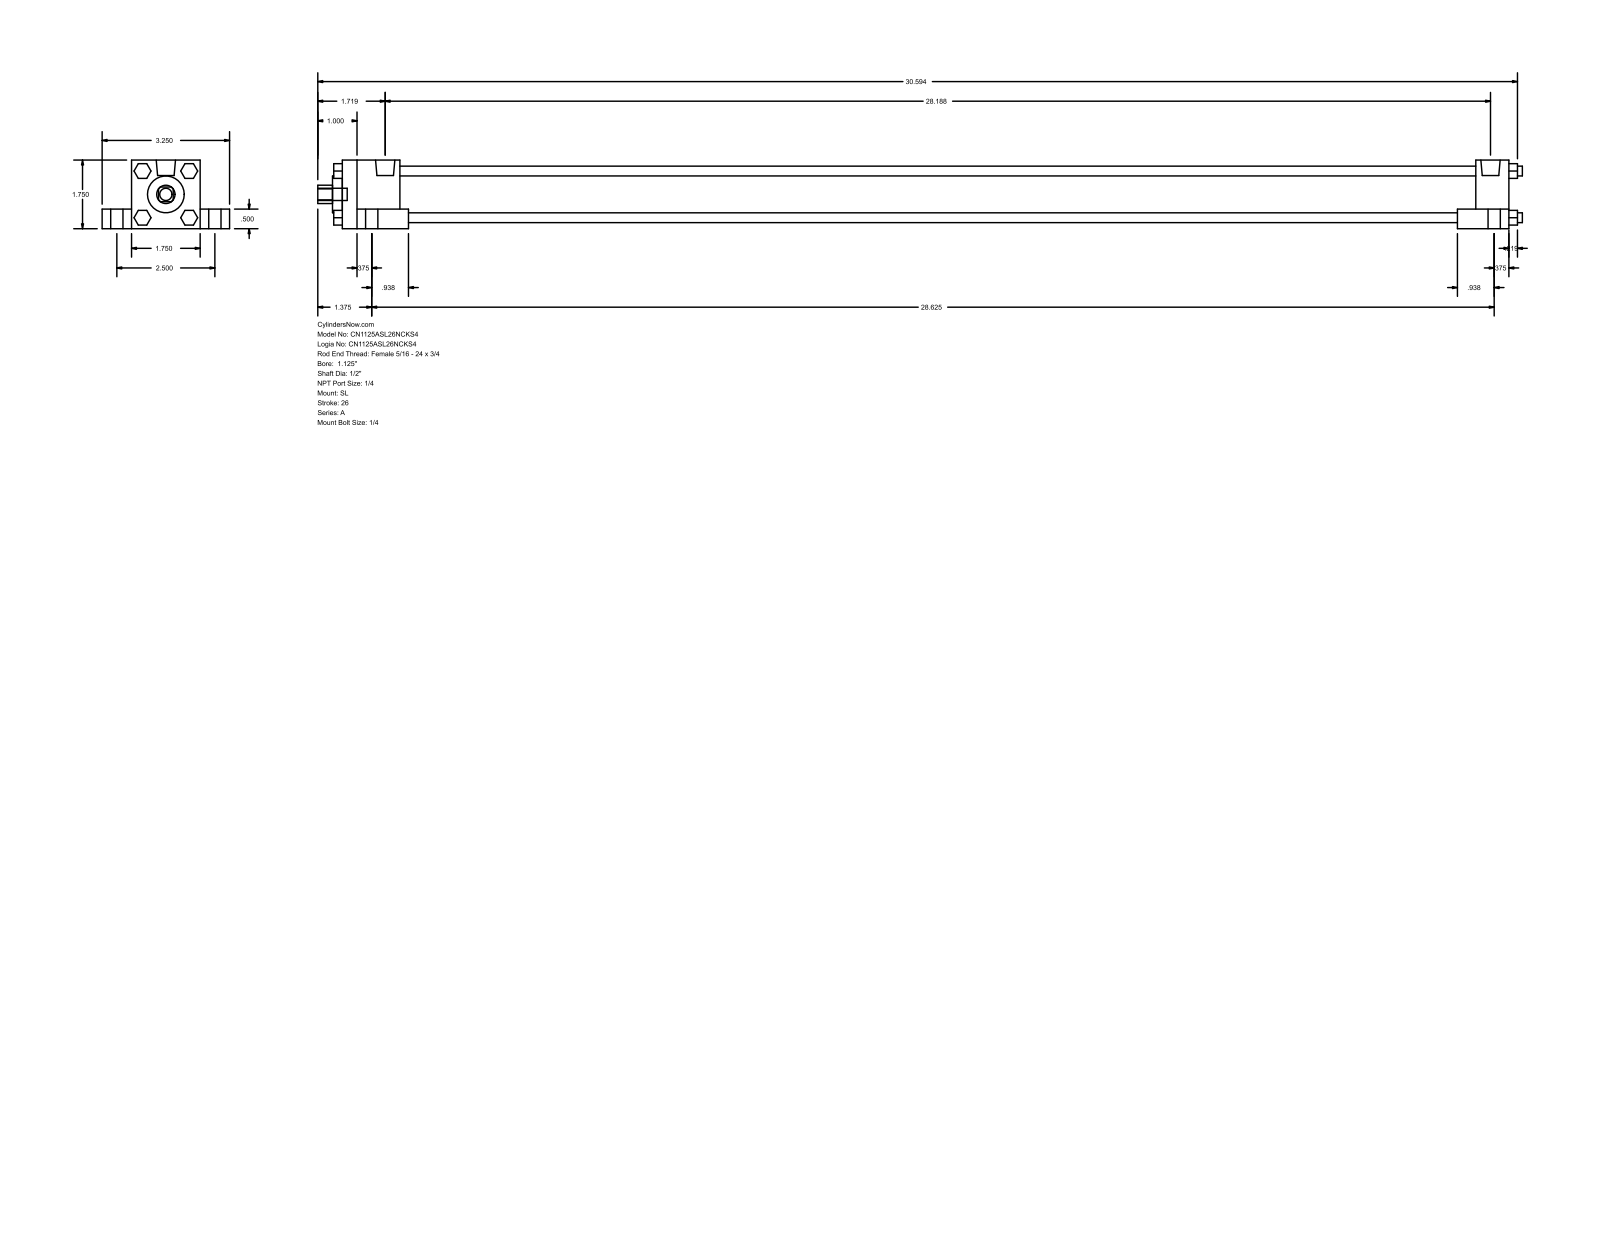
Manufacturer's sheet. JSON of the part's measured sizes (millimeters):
{"part_name": "A_SL__0112_0.5", "step_written_by": "GSSL Pune (CONFIG_CONTROL_DESIGN)", "units": "millimeters", "bodies": {"solids": 0, "faces": 150, "planar": 114, "cylindrical": 36, "other": 0}, "overall_size": [780.26, 82.55, 44.45], "round_holes": [[12.7, 1], [23.81, 1], [31.88, 1]], "round_bosses_or_shafts": [[7.94, 5], [14.29, 4], [6.35, 4], [5.56, 4], [12.49, 2]], "partial_cylinders_radius": [[5.94, 1]], "face_to_face_distances": [44.46, 31.76, 12.7, 19.04, 63.5, 718.34, 755.64, 734.21, 21.43, 37.3]}
